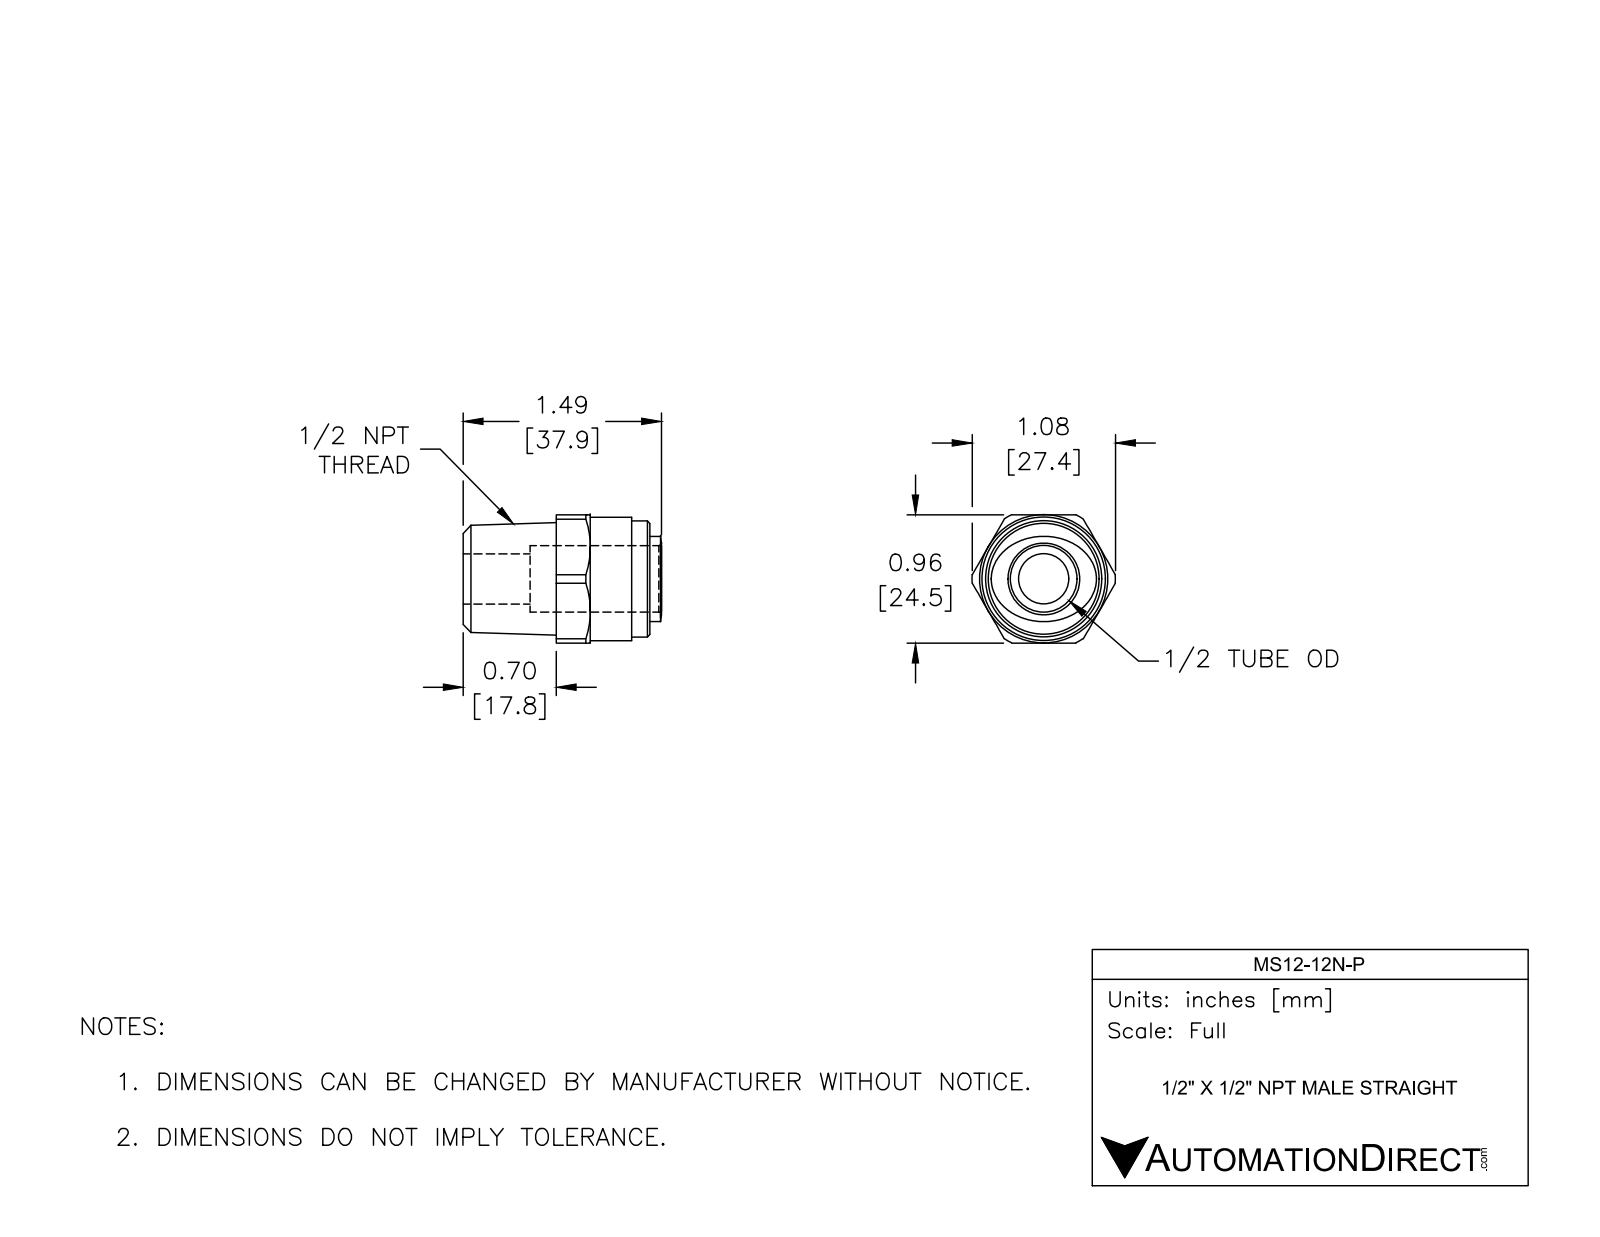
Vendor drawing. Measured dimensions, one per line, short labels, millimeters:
name: MS12-12N-P
written by: SolidWorks 2017 (AUTOMOTIVE_DESIGN)
unit: mm
bodies: 1 solid, 44 faces (12 planar, 14 cylindrical, 18 other)
size: 37.9 × 27.4 × 24.5
volume: 10 700 mm³; area: 4 793 mm²
holes: 1× ⌀9.6, 1× ⌀12.7
bosses: 1× ⌀23.6, 1× ⌀22.2
rounds: 1× R13.7
face distances: 24.5, 17.8, 35.7, 17.9, 12.8, 5, 22.9, 32.2, 19.4, 14.4
